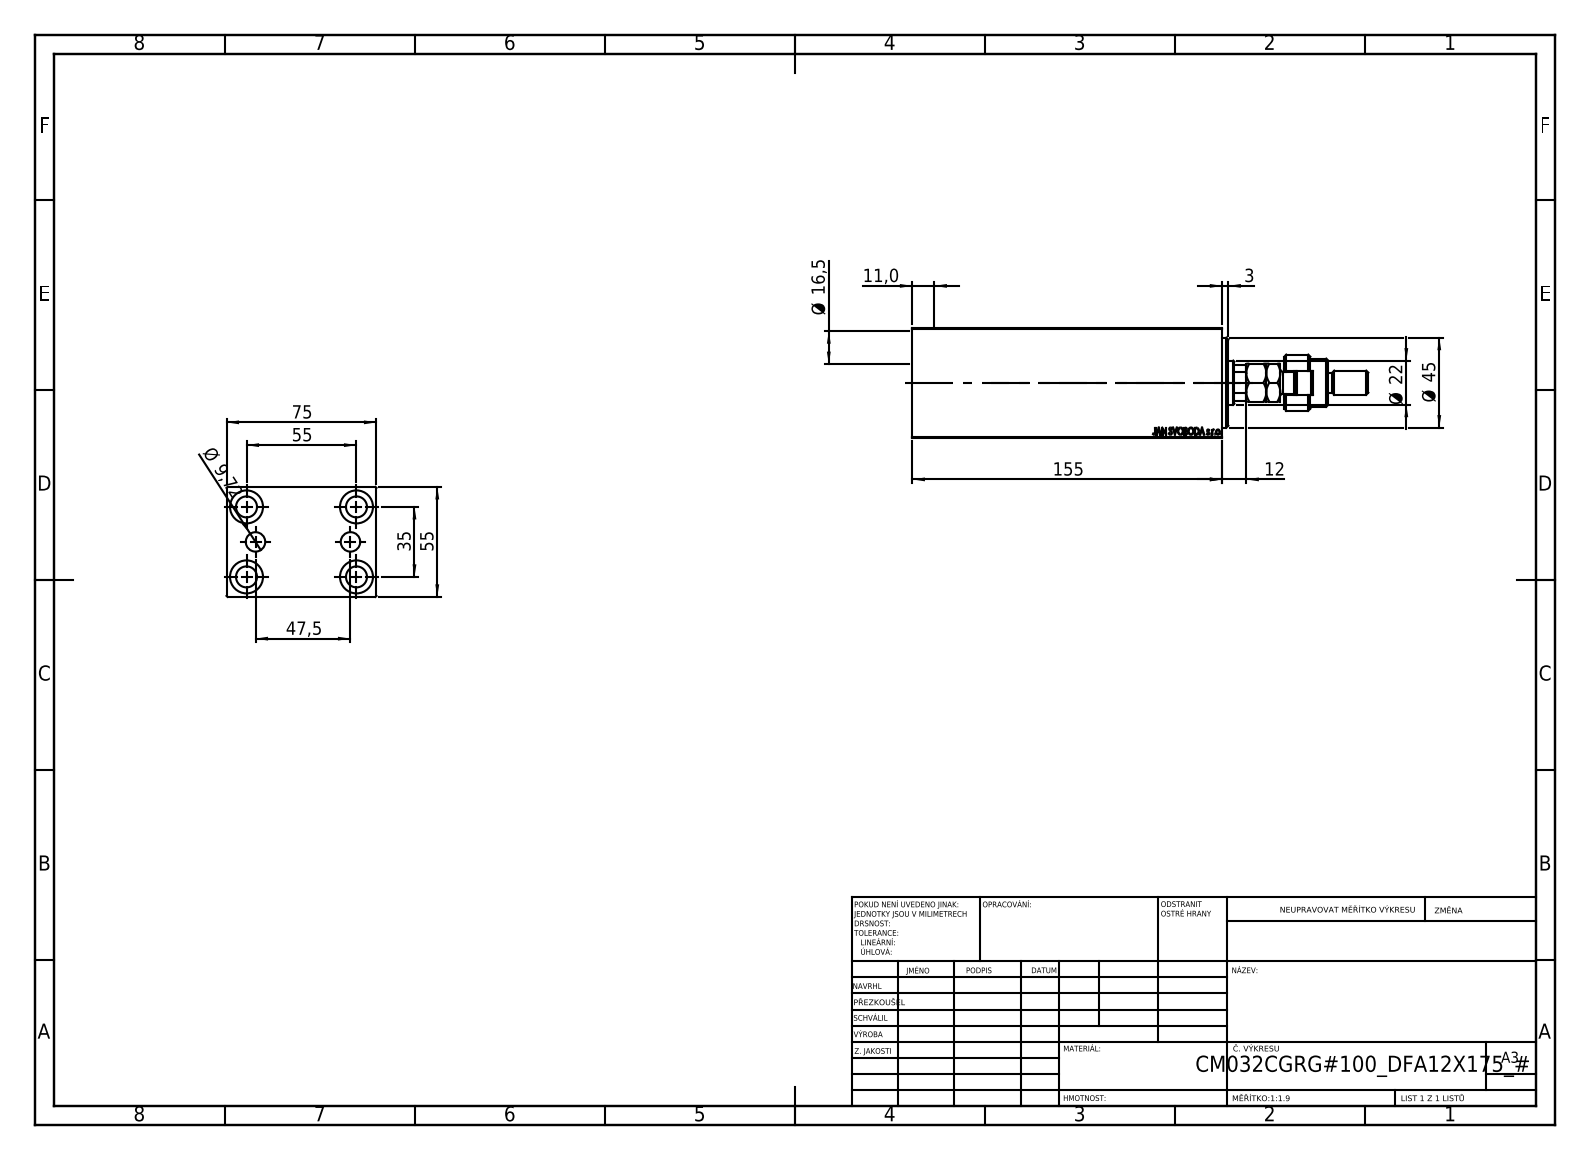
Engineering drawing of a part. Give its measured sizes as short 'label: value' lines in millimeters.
name: MFA; V450CM_C_VCP; V450CM_C_Body; V450CM_VC_B (+1 more)
written by: SolidWorks 2019 (CONFIG_CONTROL_DESIGN)
unit: mm
bodies: 5 solids, 937 faces (434 planar, 65 cylindrical, 438 other)
size: 228 × 75 × 55
volume: 554 192 mm³; area: 111 690 mm²
holes: 5× ⌀10.5, 4× ⌀16.5, 2× ⌀9.72, 1× ⌀22, 1× ⌀25.5, 1× ⌀32, 1× ⌀34, 1× ⌀45
bosses: 1× ⌀28, 1× ⌀24, 1× ⌀18, 1× ⌀12, 1× ⌀11, 1× ⌀10
rounds: 1× R9.75, 1× R10.5
face distances: 55, 75, 10, 145, 155, 8, 150, 5, 140, 12
hole spacings: 32.6, 17.76, 18.07, 35, 53.45, 54.87, 55, 65.19
